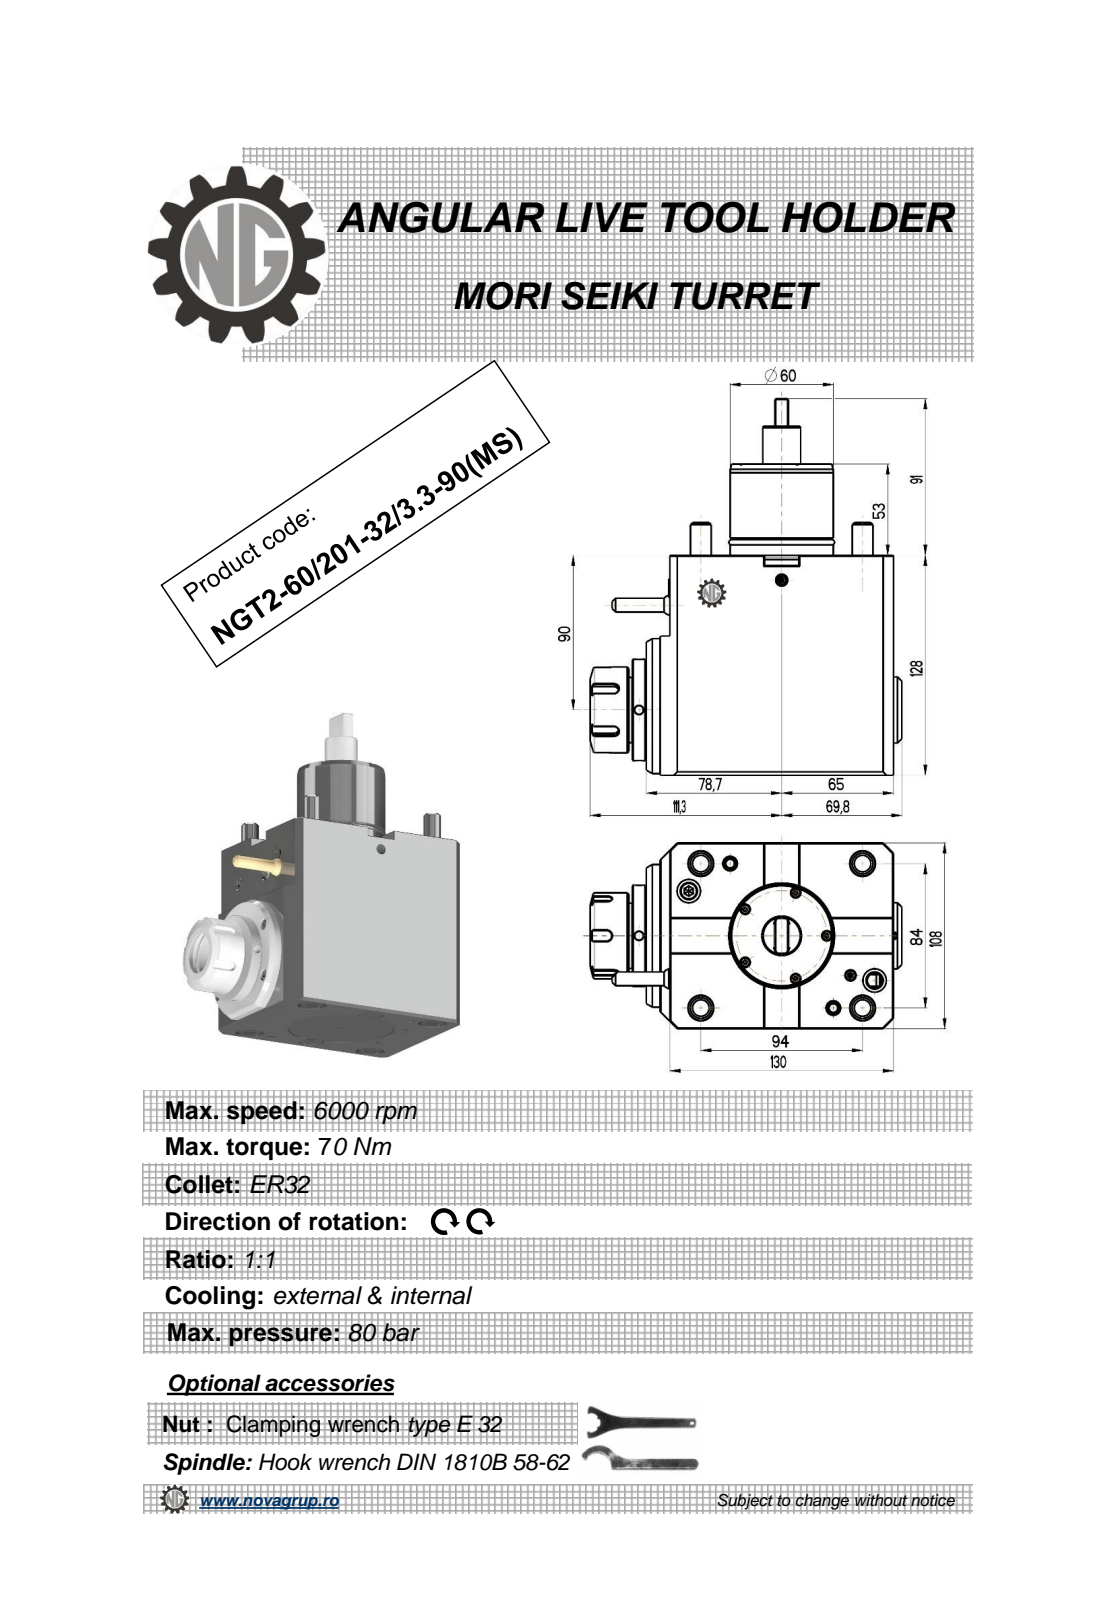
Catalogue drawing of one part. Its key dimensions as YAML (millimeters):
part_name: "NGT2_60_201_32_3_3_90_MS"
step_written_by: "PRO/ENGINEER BY PARAMETRIC TECHNOLOGY CORPORATION, 2010280 (CONFIG_CONTROL_DESIGN)"
units: millimeters
bodies: {solids: 2, faces: 338, planar: 144, cylindrical: 90, other: 104}
overall_size: [219, 181.1, 108]
volume: 2083000
surface_area: 123292
round_holes:
  - {diameter: 5, count: 3}
  - {diameter: 13.6, count: 2}
  - {diameter: 3, count: 1}
  - {diameter: 8.5, count: 1}
  - {diameter: 27, count: 1}
  - {diameter: 58, count: 1}
  - {diameter: 70, count: 1}
round_bosses_or_shafts:
  - {diameter: 12, count: 4}
  - {diameter: 83, count: 1}
  - {diameter: 60, count: 1}
  - {diameter: 59.8, count: 1}
  - {diameter: 59, count: 1}
  - {diameter: 57.4, count: 1}
  - {diameter: 55.4, count: 1}
  - {diameter: 50, count: 1}
partial_cylinders:
  - {radius: 0.22, count: 6}
  - {radius: 0.51, count: 6}
  - {radius: 3, count: 5}
  - {radius: 0.8, count: 2}
  - {radius: 10.75, count: 1}
face_to_face_distances: [108, 128, 130, 6, 8, 13.7, 143.7, 122, 53, 59]
hole_center_spacings: [59.93, 38.91, 65.92, 82.95, 119.87, 139.4]
